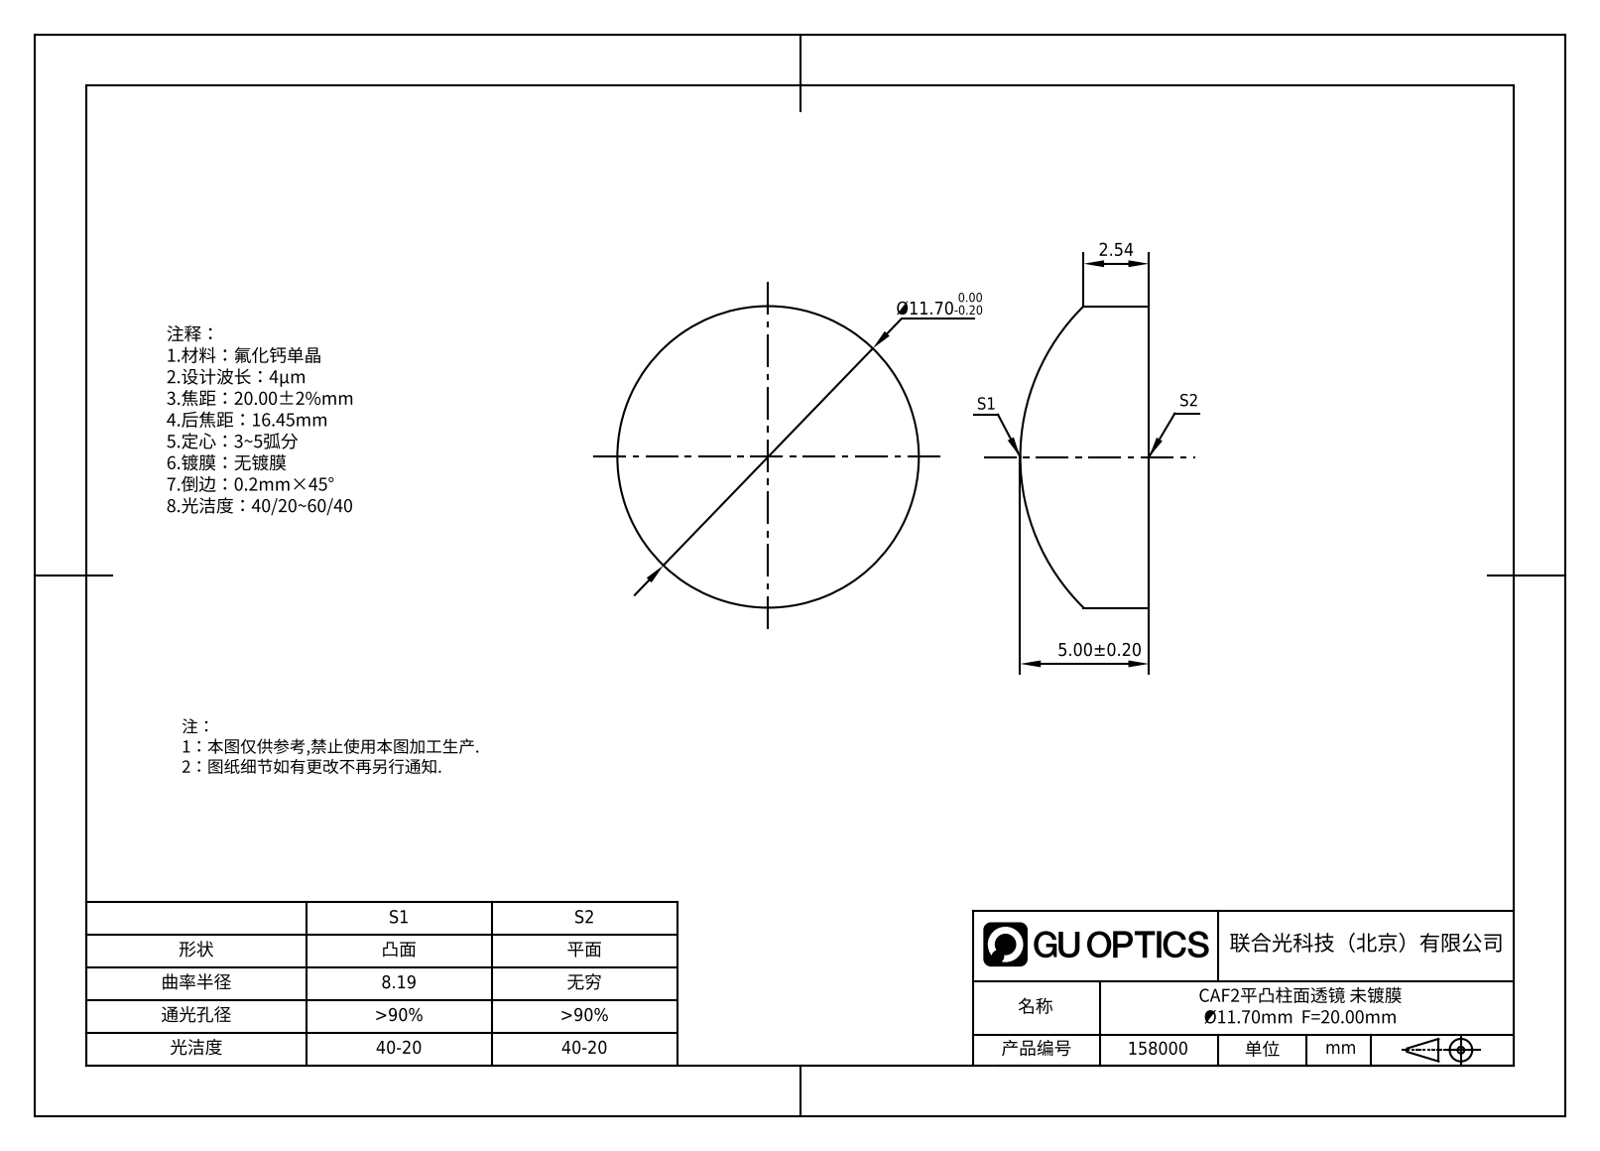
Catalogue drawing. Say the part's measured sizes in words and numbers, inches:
The part is named "GL55-012-020". Its 3-D file was written by "SolidWorks 2022 (AUTOMOTIVE_DESIGN)". It is 1 solid with 9 faces: 1 planar, 4 cylindrical and 4 other. Overall it measures 0.461 by 0.461 by 0.197 inches. Its volume is 0.029 cubic inches and its surface area 0.555 square inches. Round bosses or shafts: 1 of diameter 0.461. Partial cylindrical surfaces (rounded edges, fillets, slot ends): 1 of radius 0.322.
